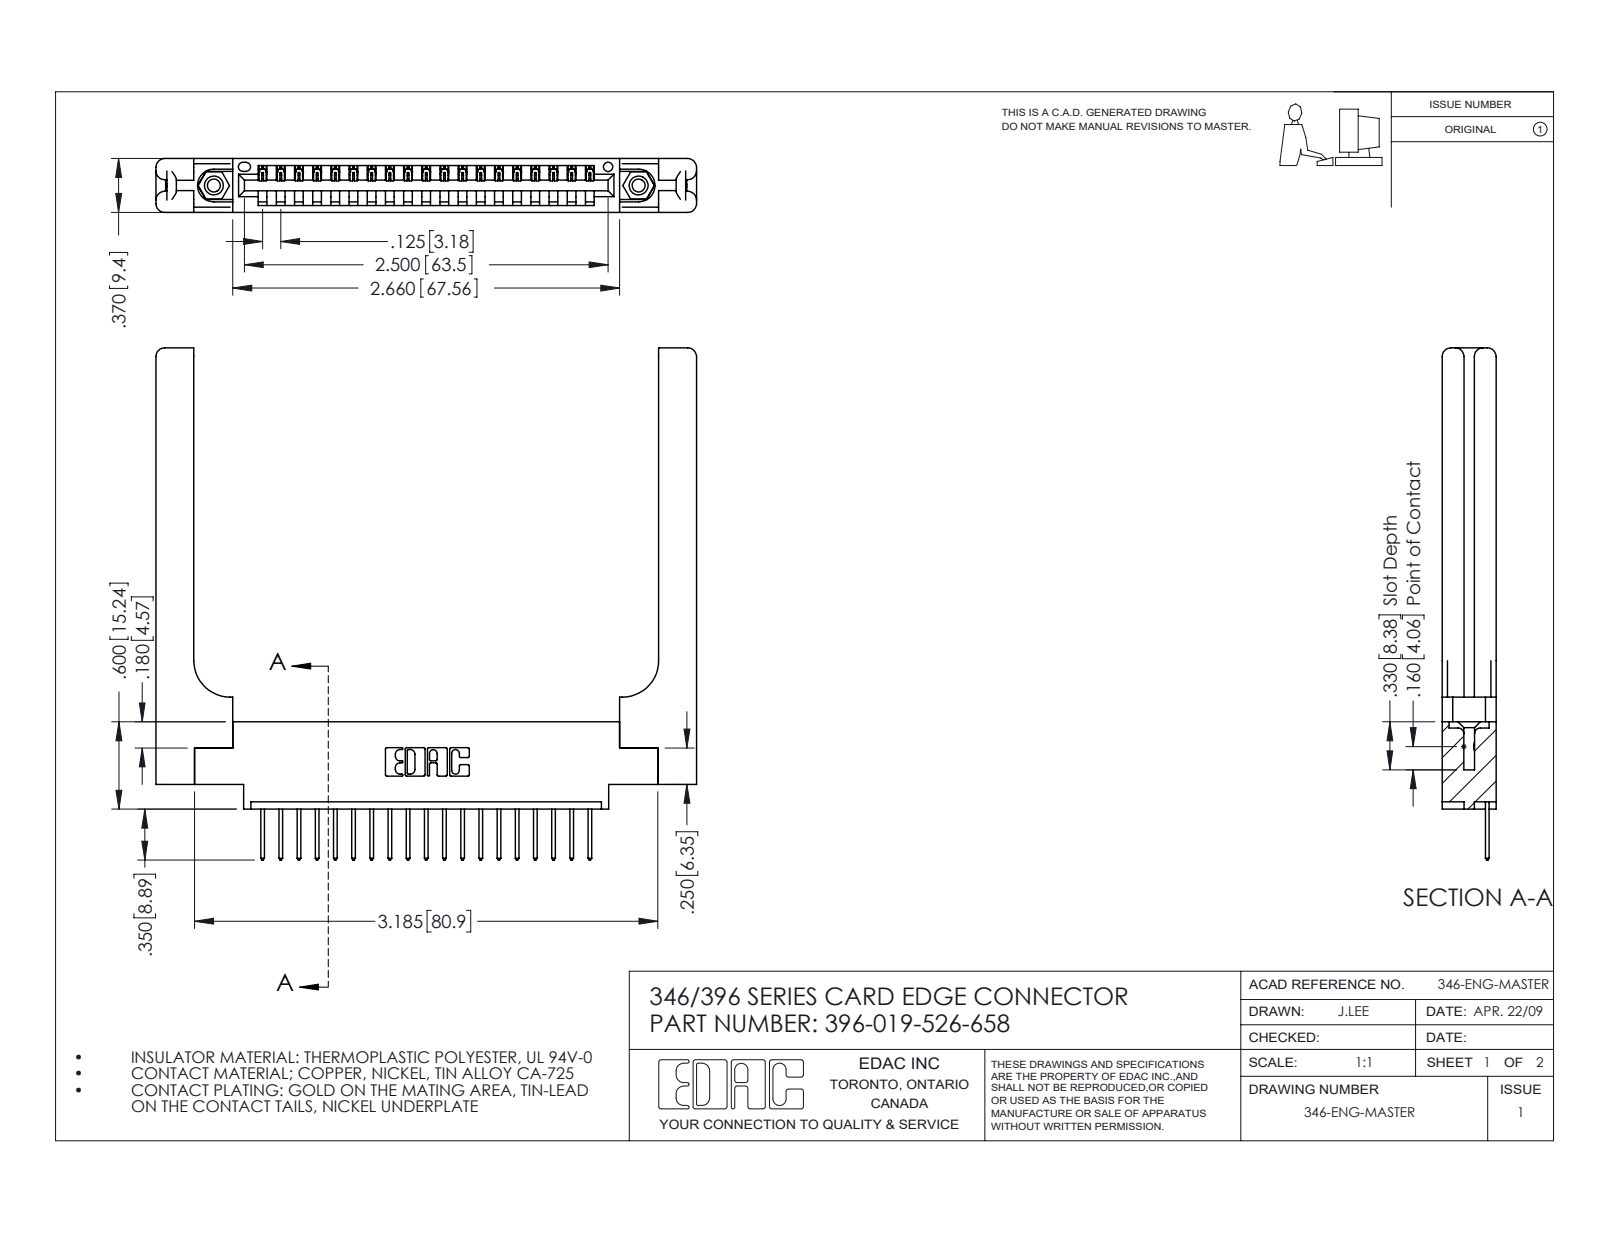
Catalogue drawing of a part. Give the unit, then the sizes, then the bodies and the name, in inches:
Units: inches
Overall size (bounding box): 3.716 × 3.52 × 0.37
Round holes (diameter × count): ⌀0.089 ×2, ⌀0.125 ×2, ⌀0.156 ×2, ⌀0.064 ×1
Round bosses / shafts (diameter × count): ⌀0.155 ×2
Partial cylindrical surfaces — rounded edges, fillets, slot ends (radius × count): R0.006 ×38, R0.01 ×38, R0.01 ×22, R0.06 ×16, R0.007 ×6, R0.031 ×6, R0.026 ×3, R0.03 ×2
Main face-to-face distances: 0.37, 0.072, 0.15, 0.148, 0.048, 0.322, 0.25, 0.102, 0.22, 0.173
Hole centre spacings: 0.246, 2.713, 2.92
Volume: 0.99 in³ · Surface area: 24.72 in²
Bodies: 24 solids, 1484 faces (988 planar, 436 cylindrical, 60 other)
Part name (STEP PRODUCT): 396-019-526-658; 346-220-058_345-220-058; 346 Part_0.170 Offset - 0.156 Dia-TH; 345-292-001_345-293-126 (+1 more)
STEP written by: SolidWorks 2016 (CONFIG_CONTROL_DESIGN)
